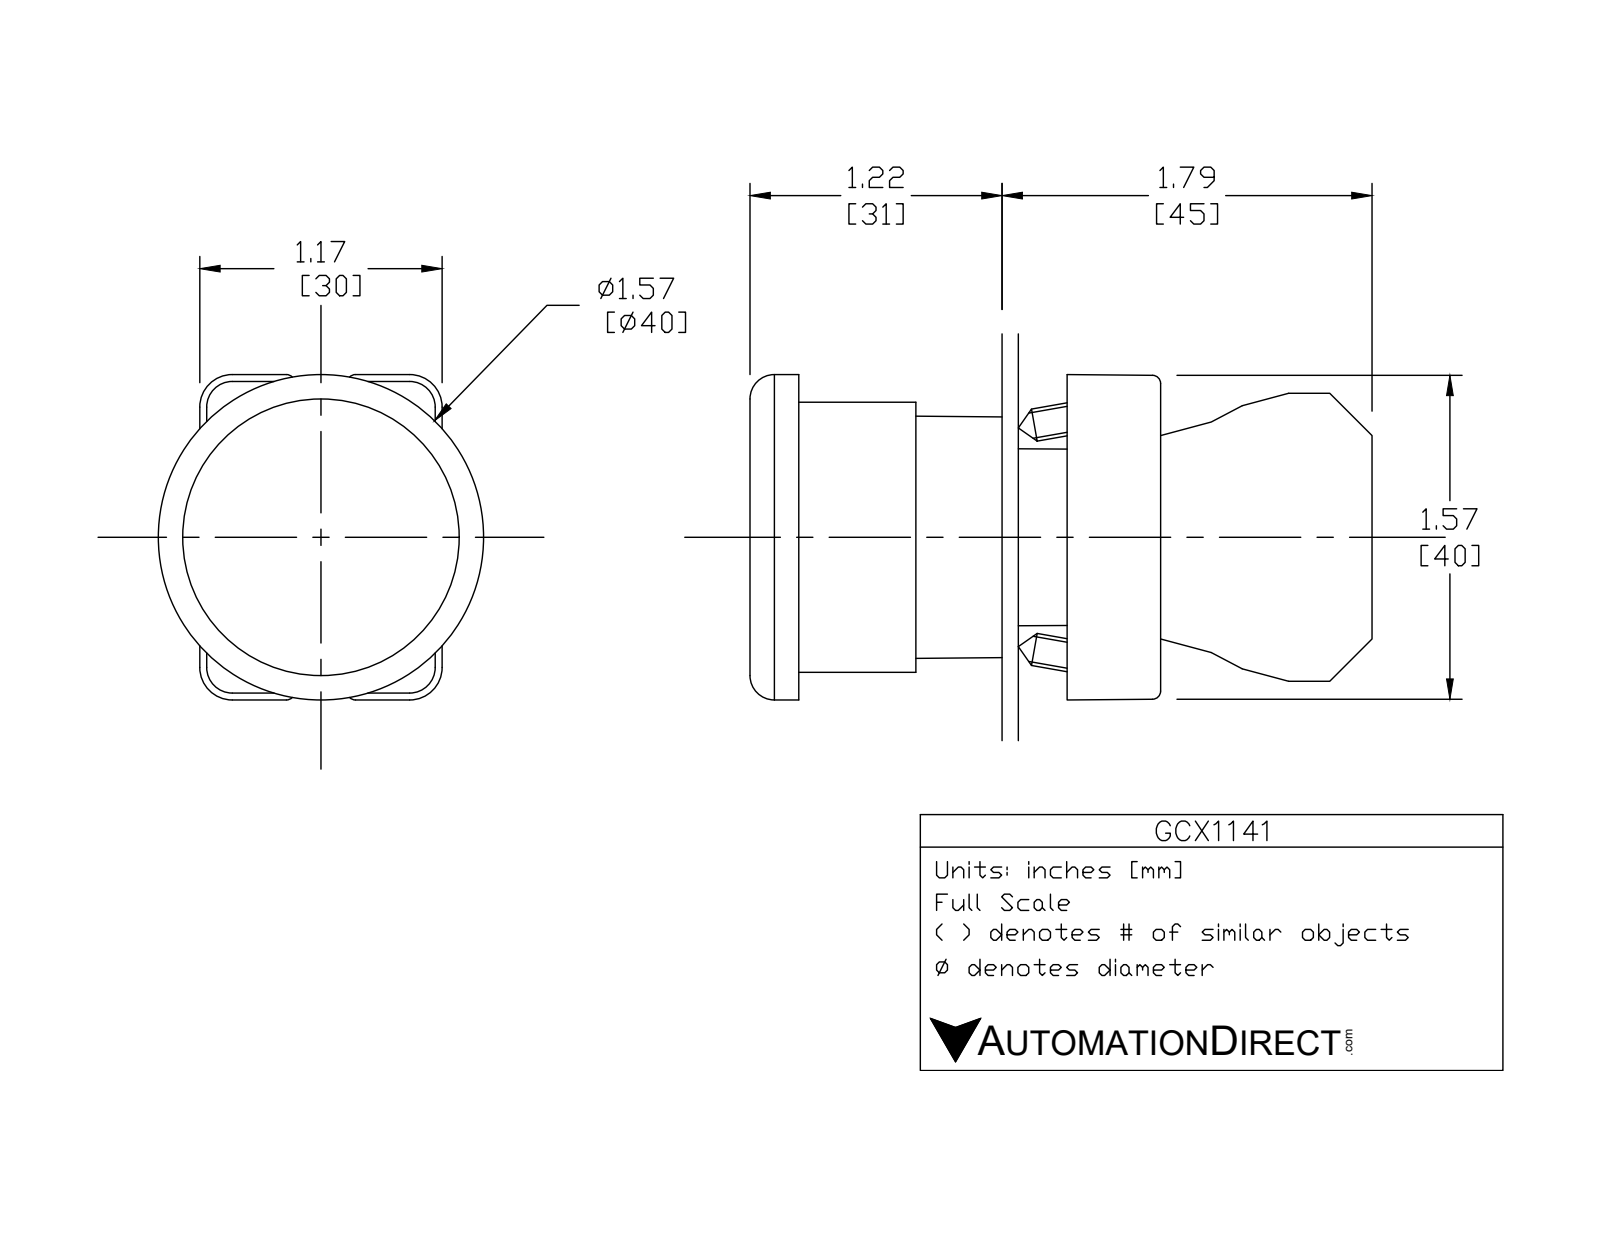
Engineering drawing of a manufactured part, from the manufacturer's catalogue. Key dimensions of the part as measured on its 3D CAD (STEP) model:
Part name (STEP PRODUCT): GCX1141; ecx1030; ECX1029-2; GCX1141 OPERATOR
STEP written by: SolidWorks 2016 (AUTOMOTIVE_DESIGN)
Units: inches
Bodies: 7 solids, 399 faces (230 planar, 140 cylindrical, 29 other)
Overall size (bounding box): 2.944 × 1.581 × 1.575
Volume: 1.863 in³ · Surface area: 34.45 in²
Round holes (diameter × count): ⌀0.079 ×2, ⌀0.124 ×2, ⌀0.13 ×2, ⌀0.087 ×1, ⌀0.197 ×1, ⌀0.795 ×1, ⌀0.878 ×1, ⌀0.888 ×1, ⌀1.024 ×1, ⌀1.181 ×1
Round bosses / shafts (diameter × count): ⌀0.157 ×2, ⌀1.575 ×1, ⌀1.299 ×1, ⌀1.175 ×1, ⌀0.945 ×1, ⌀0.856 ×1, ⌀0.787 ×1, ⌀0.78 ×1
Partial cylindrical surfaces — rounded edges, fillets, slot ends (radius × count): R0.059 ×24, R0.041 ×12, R0.124 ×12, R0.157 ×12, R0.039 ×4, R0.128 ×2, R0.02 ×1, R0.063 ×1
Main face-to-face distances: 1.921, 0.579, 0.033, 1.763, 0.157, 1.724, 0.031, 1.024, 0.76, 1.004
Hole centre spacings: 0.236, 0.544, 0.472, 0.49
